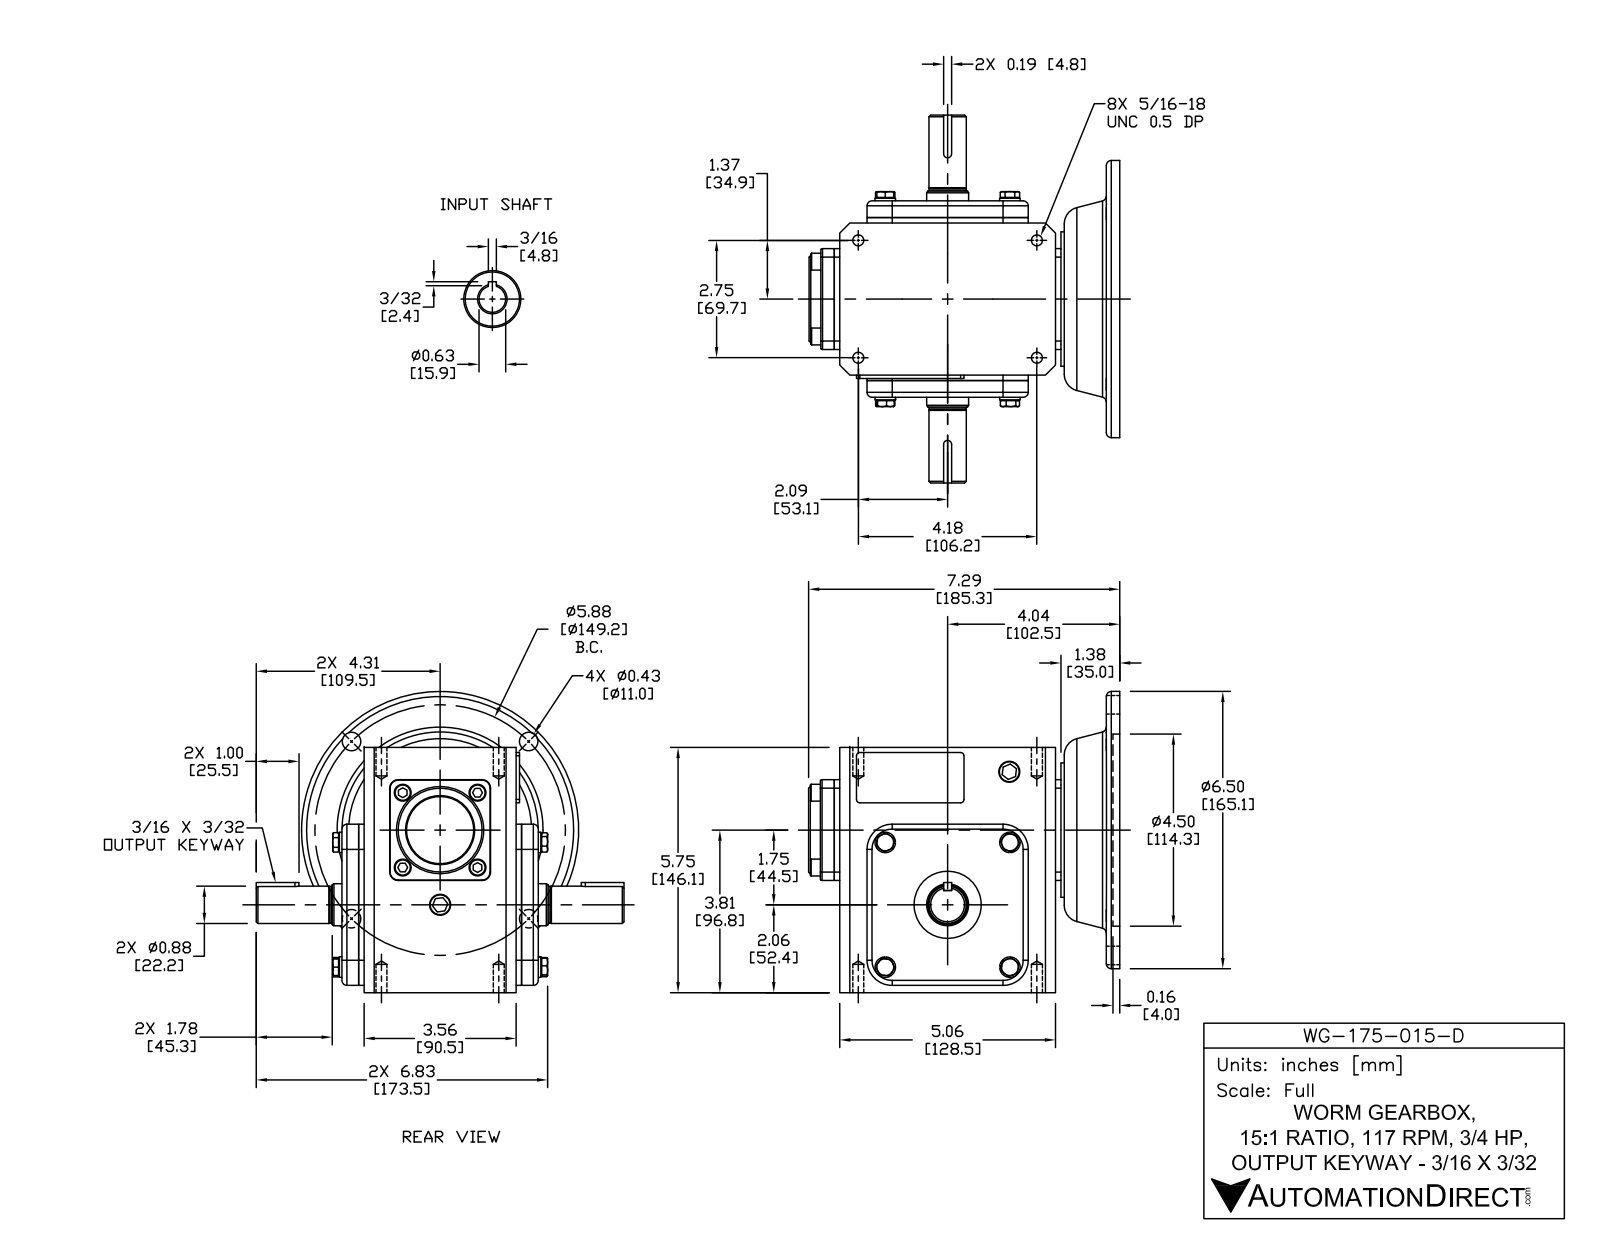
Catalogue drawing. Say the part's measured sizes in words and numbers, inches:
The part is named "WG-175-015-D". Its 3-D file was written by "SolidWorks 2015 (CONFIG_CONTROL_DESIGN)". It is 45 solids with 647 faces: 324 planar, 186 cylindrical and 137 other. Overall it measures 8.622 by 7.283 by 7.06 inches. Its volume is 133.1 cubic inches and its surface area 375.6 square inches. Round holes: 4 of diameter 0.257, 4 of diameter 0.406, 1 of diameter 0.512, 1 of diameter 0.625, 1 of diameter 0.984, 1 of diameter 1.181, 1 of diameter 1.457, 1 of diameter 1.575, 1 of diameter 3.543, 1 of diameter 4.5. Round bosses or shafts: 8 of diameter 0.394, 4 of diameter 0.48, 2 of diameter 0.512, 1 of diameter 6.496, 1 of diameter 3.15, 1 of diameter 2.047, 1 of diameter 1.575, 1 of diameter 0.875. Partial cylindrical surfaces (rounded edges, fillets, slot ends): 8 of radius 0.079, 8 of radius 0.118, 4 of radius 0.197, 4 of radius 0.591, 2 of radius 0.02, 2 of radius 0.039, 2 of radius 0.094. The main face-to-face distances are 0.128, 3.819, 4.213, 0.394, 4.085, 3.691, 0.522, 0.315, 5.75, 6.693. The hole center spacings are 2.937, 4.154, 2.103, 2.75, 4.188, 4.354, 5.01, 5.875.
